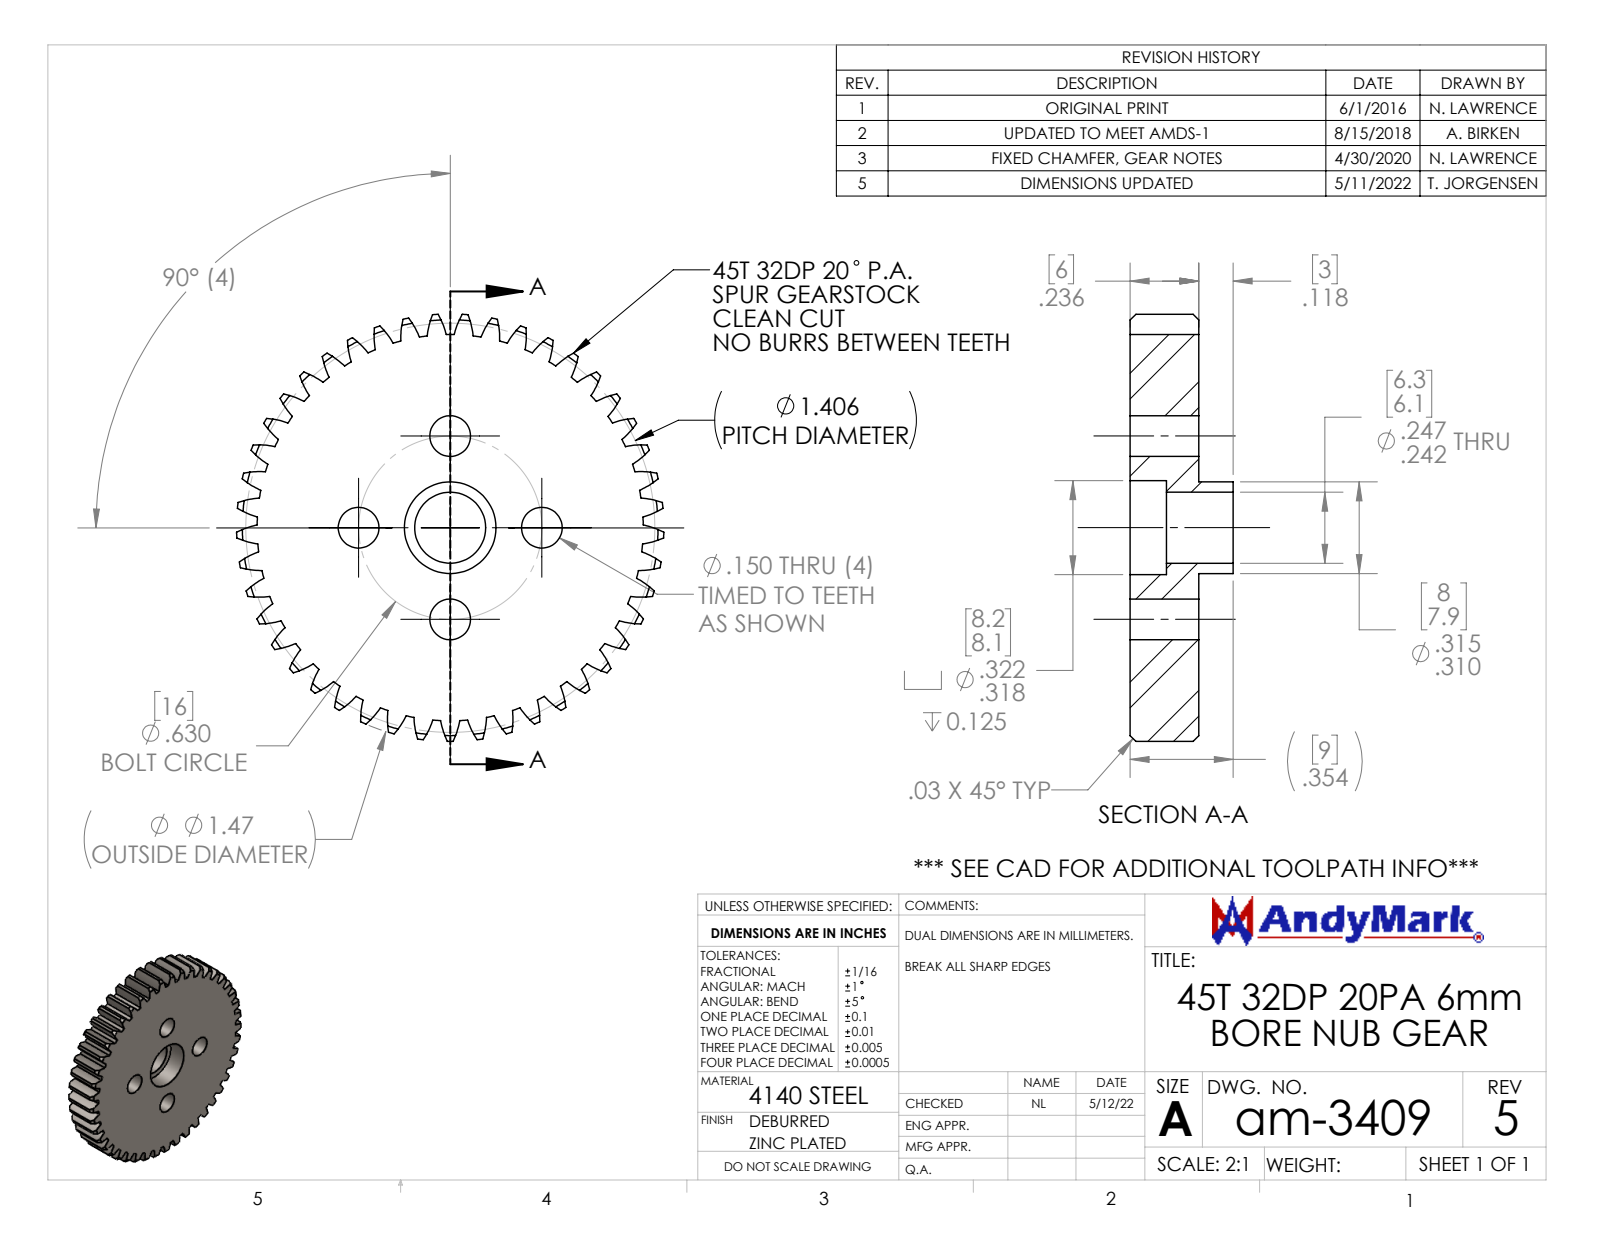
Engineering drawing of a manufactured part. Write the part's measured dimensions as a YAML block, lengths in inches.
part_name: "45T 32DP 6mm Bore Nub Gear"
step_written_by: "SolidWorks 2021 (CONFIG_CONTROL_DESIGN)"
units: inches
bodies: {solids: 1, faces: 292, planar: 4, cylindrical: 198, other: 90}
overall_size: [1.468, 1.468, 0.354]
volume: 0.335
surface_area: 5.725
round_holes:
  - {diameter: 0.14, count: 4}
  - {diameter: 0.244, count: 1}
  - {diameter: 0.323, count: 1}
round_bosses_or_shafts:
  - {diameter: 0.315, count: 1}
partial_cylinders:
  - {radius: 0.281, count: 90}
  - {radius: 0.664, count: 1}
  - {radius: 0.734, count: 1}
face_to_face_distances: [0.236, 0.125, 0.111, 0.354, 0.23, 0.118]
hole_center_spacings: [0.315, 0.445, 0.63]
